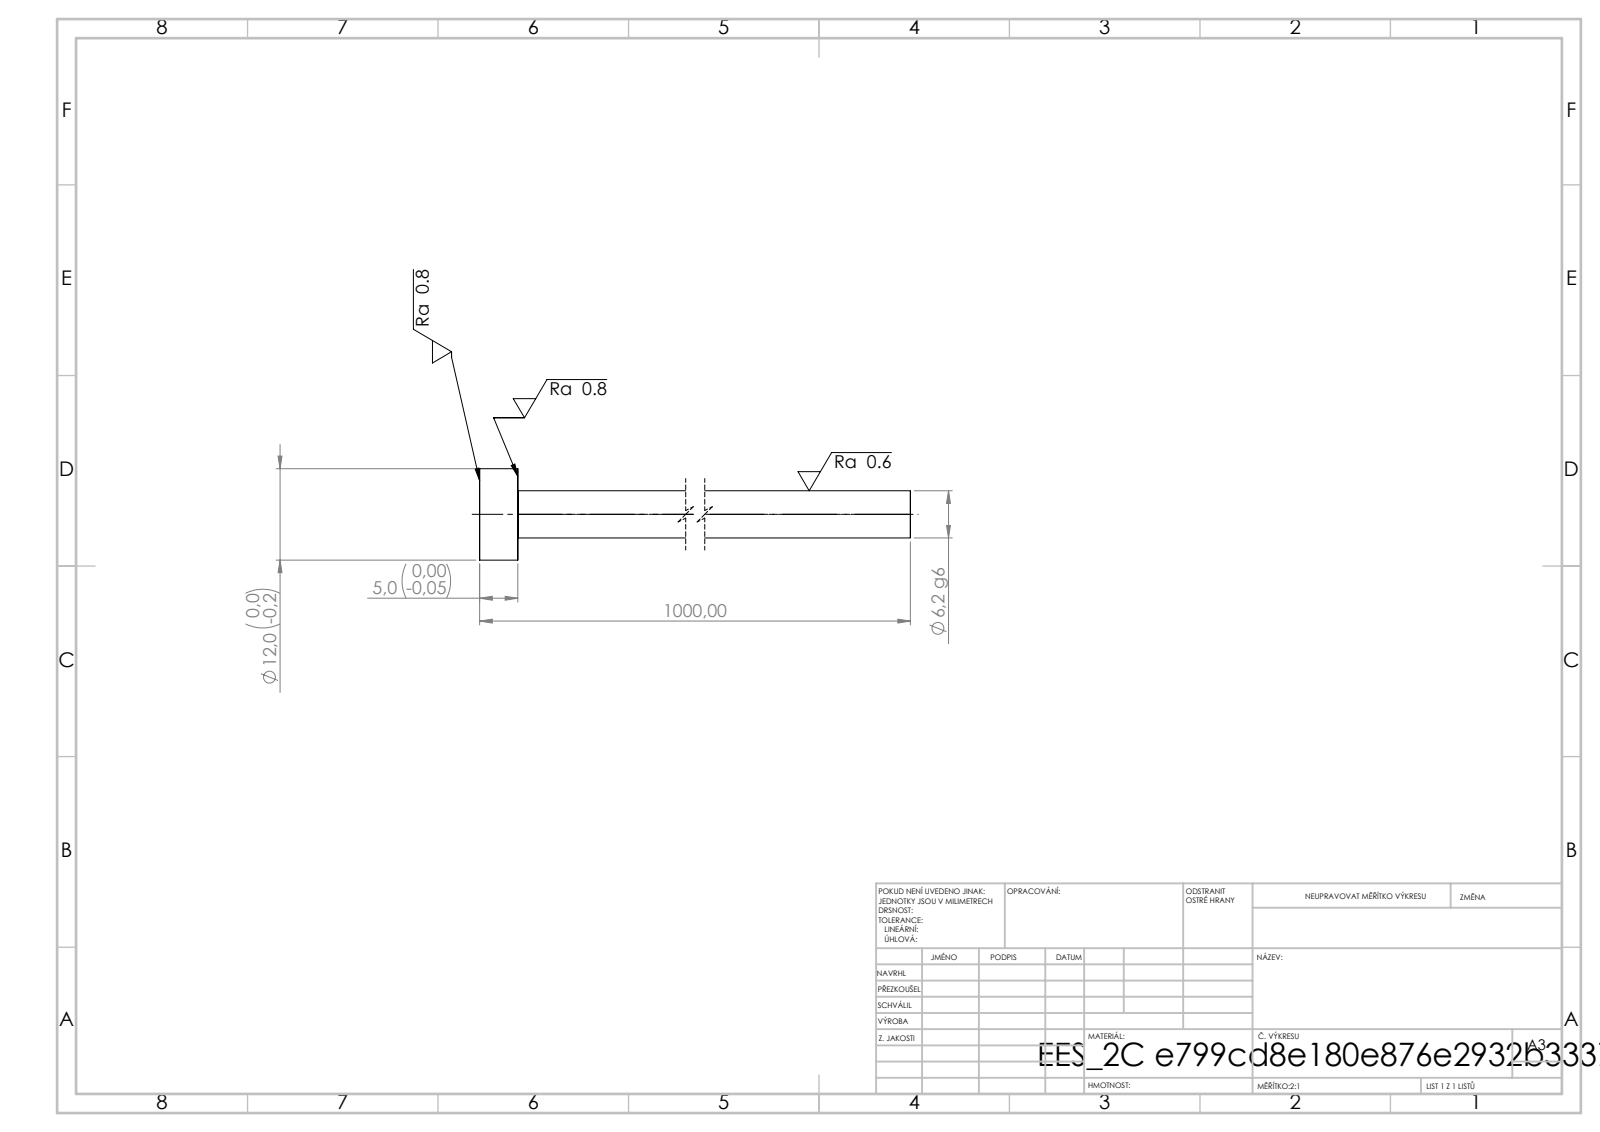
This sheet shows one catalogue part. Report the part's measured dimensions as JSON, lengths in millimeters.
{"step_written_by": "SolidWorks 2019 (CONFIG_CONTROL_DESIGN)", "units": "millimeters", "bodies": {"solids": 1, "faces": 7, "planar": 3, "cylindrical": 4, "other": 0}, "overall_size": [1000, 12, 12], "volume_mm3": 30605, "surface_area_mm2": 19795, "round_bosses_or_shafts": [[12, 1], [6.2, 1]], "face_to_face_distances": [5, 1000, 995]}
